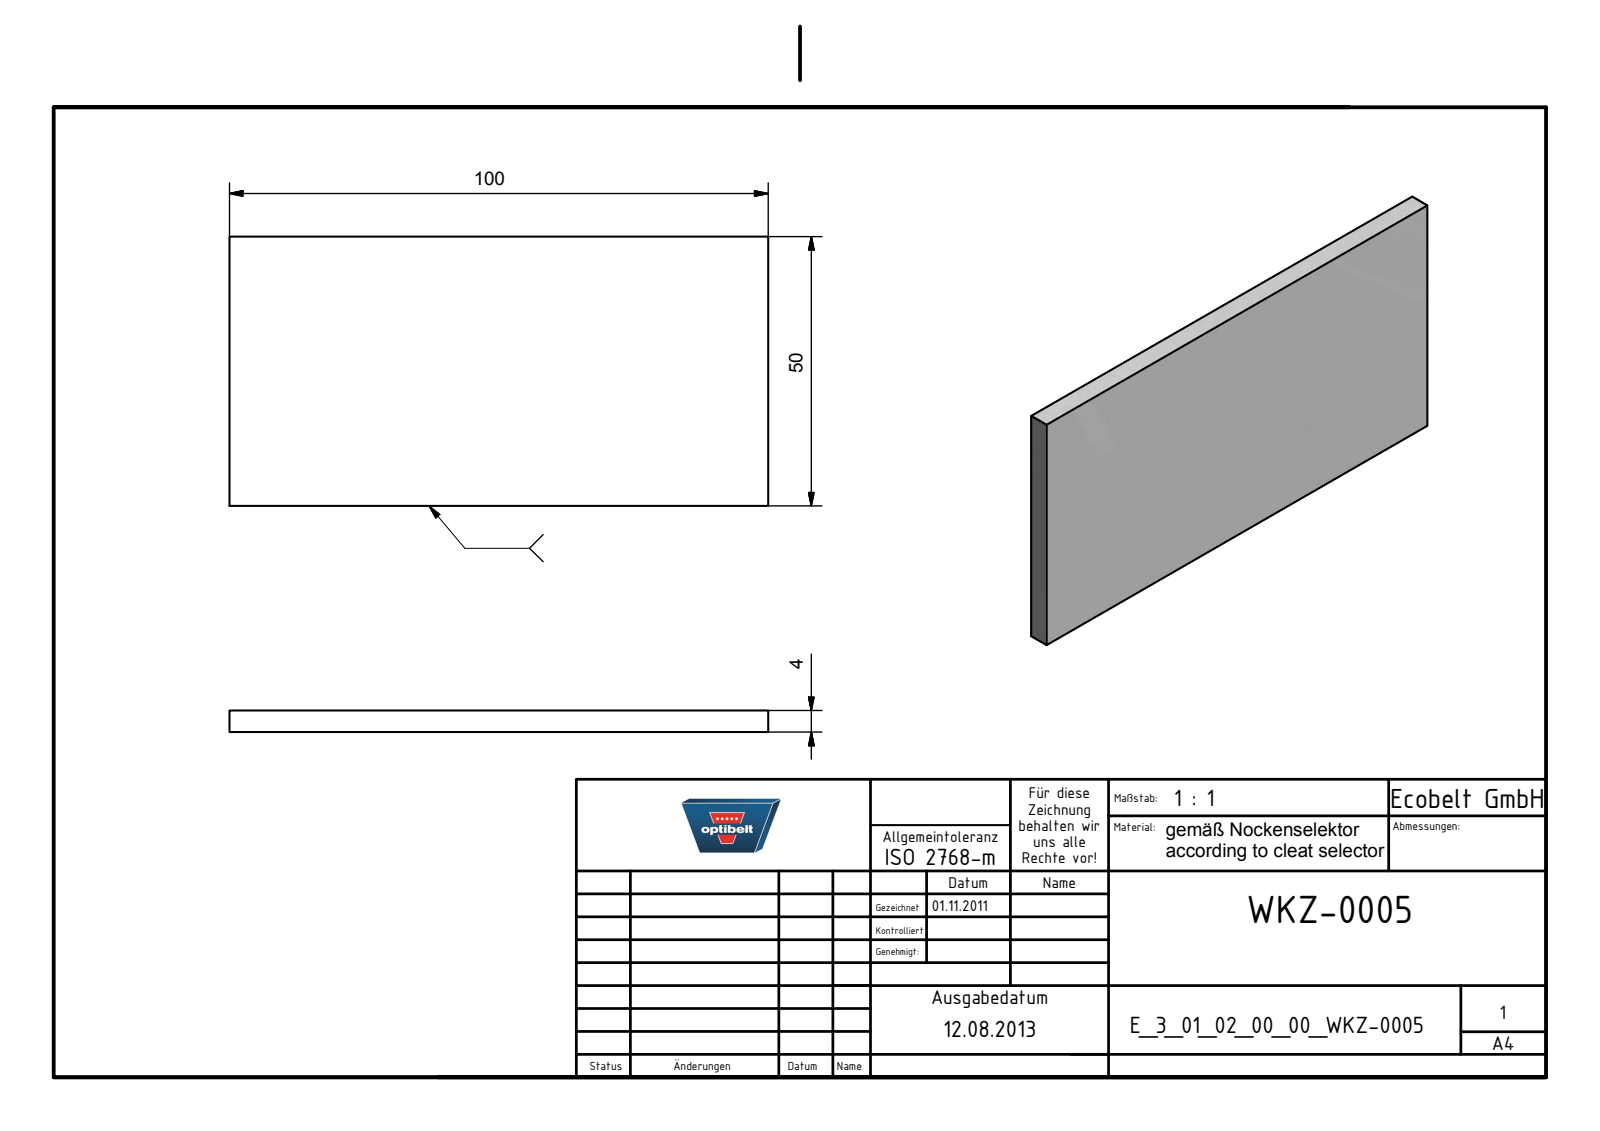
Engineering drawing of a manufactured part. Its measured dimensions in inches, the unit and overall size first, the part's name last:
Units: inches
Overall size (bounding box): 3.937 × 1.969 × 0.157
Main face-to-face distances: 0.157, 1.969, 3.937
Volume: 1.22 in³ · Surface area: 17.36 in²
Bodies: 1 solid, 6 faces (6 planar, 0 cylindrical, 0 other)
Part name (STEP PRODUCT): E_3_01_02_00_00_WKZ-0005
STEP written by: Autodesk Inventor 2021 (AUTOMOTIVE_DESIGN)
